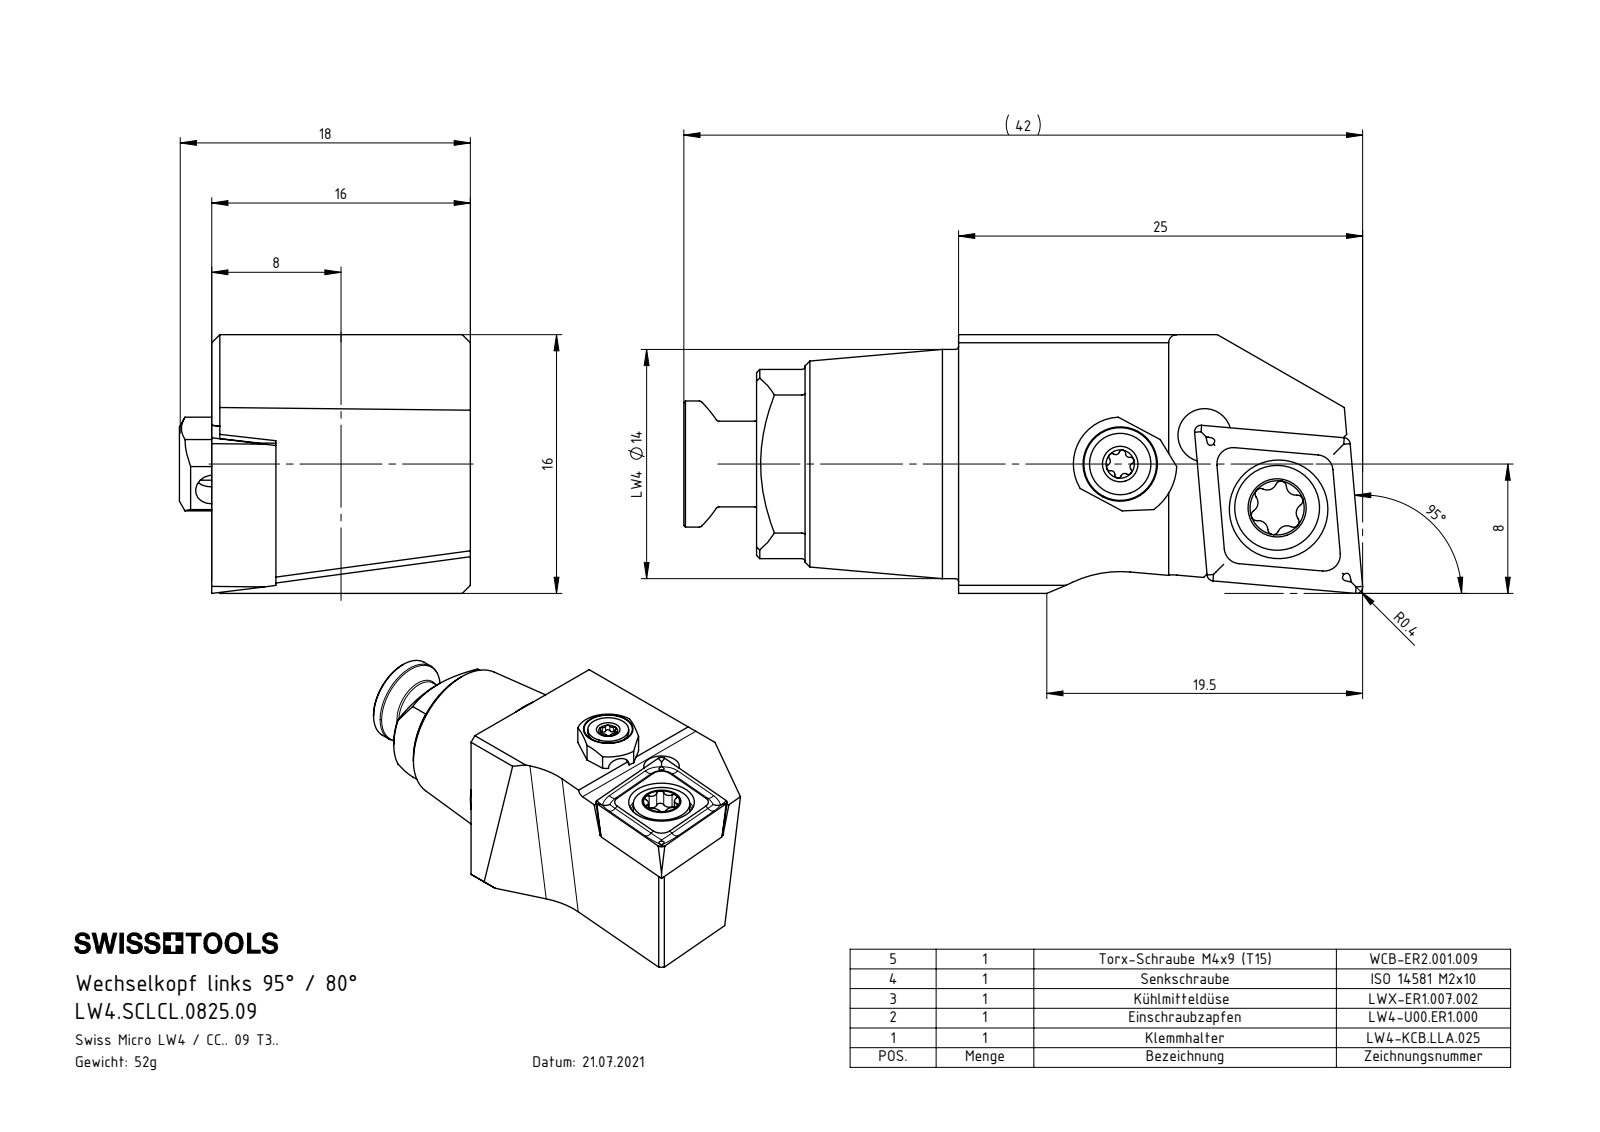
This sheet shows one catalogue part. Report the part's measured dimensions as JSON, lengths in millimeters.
{"part_name": "LW4.SCLCL.0825.09; ISO 14581 - M2x10; LWX-ER1.007.002; LW4-U00.ER1.000_B (+3 more)", "step_written_by": "SolidWorks 2022 (CONFIG_CONTROL_DESIGN)", "units": "millimeters", "bodies": {"solids": 6, "faces": 262, "planar": 69, "cylindrical": 80, "other": 113}, "overall_size": [42, 18, 16], "volume_mm3": 6656, "surface_area_mm2": 3871, "round_holes": [[3, 2], [3.3, 2], [1.6, 1], [2, 1], [2.5, 1], [4.4, 1], [5.5, 1], [6.1, 1]], "round_bosses_or_shafts": [[14.17, 1], [7.7, 1], [6, 1], [5.3, 1], [5.25, 1], [5, 1], [4, 1], [3.8, 1]], "partial_cylinders_radius": [[0.2, 8], [0.24, 6], [0.34, 6], [0.59, 6], [0.5, 1], [1, 1], [2.9, 1], [3.5, 1]], "face_to_face_distances": [16, 12.03, 3.97, 15.5, 3.47, 0.5, 7.5, 2, 3, 12.5], "hole_center_spacings": [5.52, 6.35, 6.48, 10.08, 10.19]}
